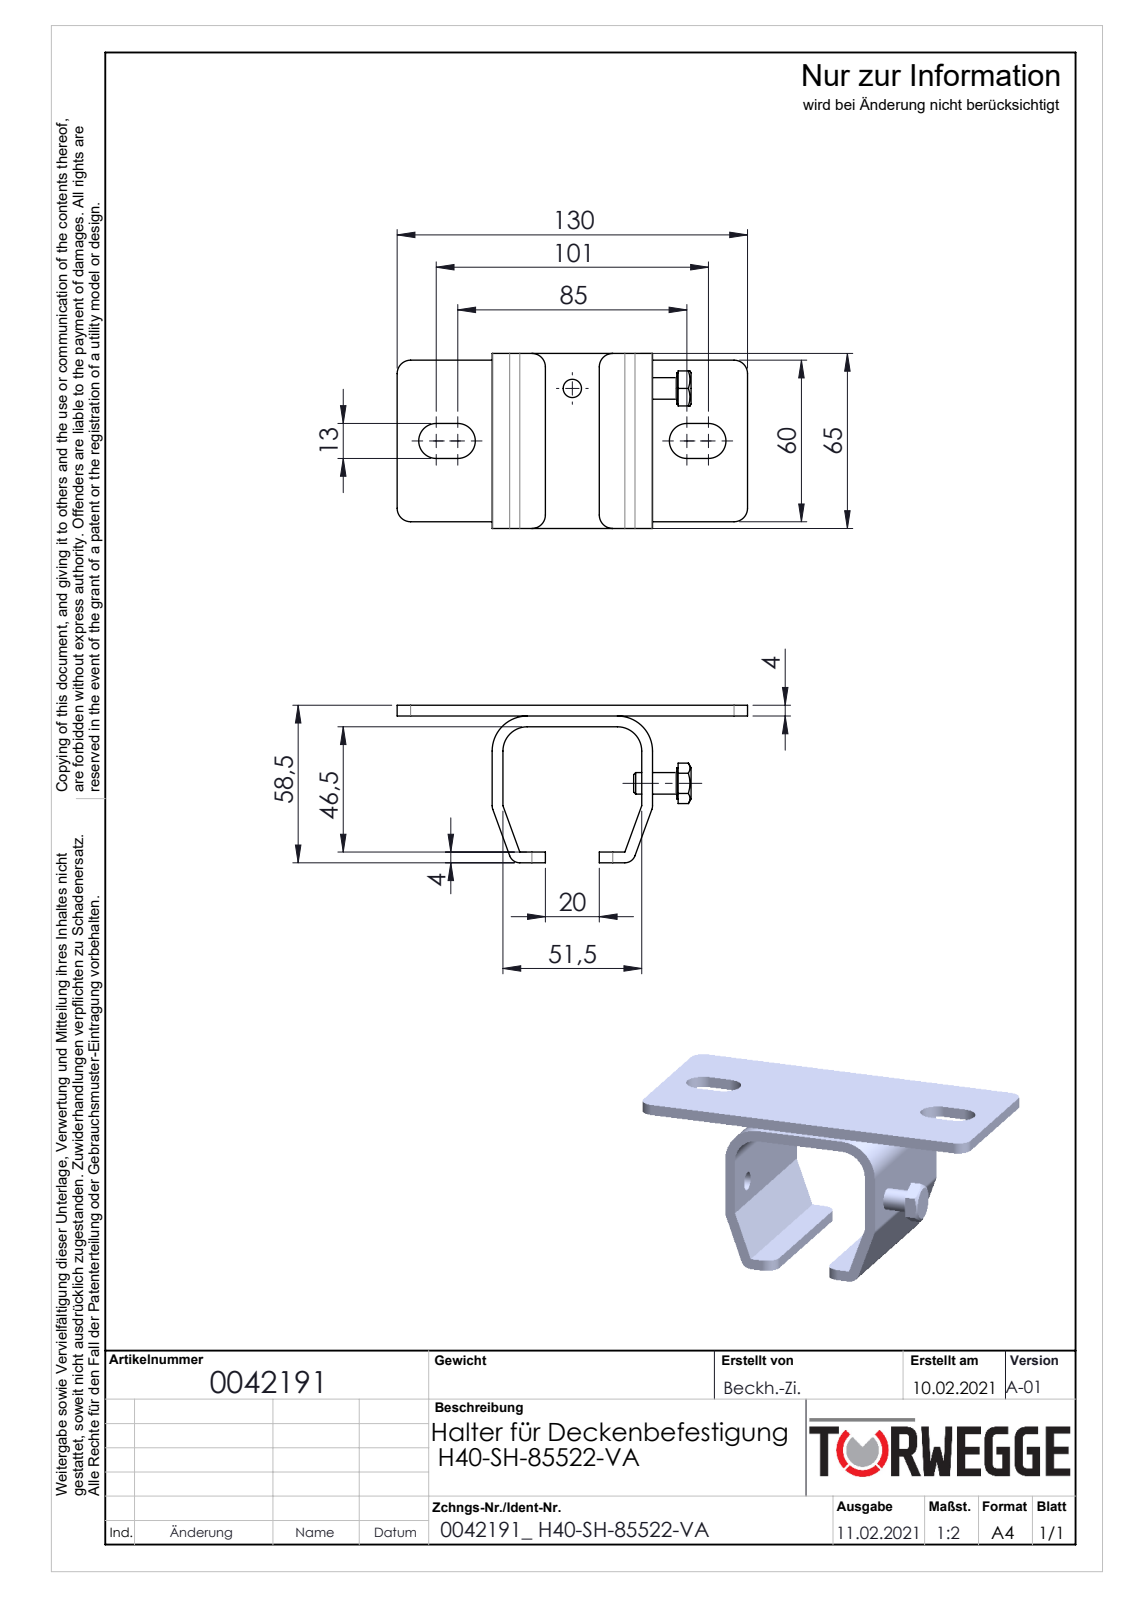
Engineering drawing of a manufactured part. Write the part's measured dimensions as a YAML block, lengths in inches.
part_name: "0042191"
step_written_by: "SolidWorks 2020 (AUTOMOTIVE_DESIGN)"
units: inches
bodies: {solids: 3, faces: 76, planar: 38, cylindrical: 32, other: 6}
overall_size: [5.118, 2.559, 2.303]
volume: 4.551
surface_area: 64.26
round_holes:
  - {diameter: 0.268, count: 2}
round_bosses_or_shafts:
  - {diameter: 0.457, count: 1}
  - {diameter: 0.315, count: 1}
partial_cylinders:
  - {radius: 0.197, count: 8}
  - {radius: 0.157, count: 4}
  - {radius: 0.256, count: 4}
  - {radius: 0.354, count: 2}
  - {radius: 0.512, count: 2}
face_to_face_distances: [0.157, 2.185, 1.988, 2.146, 0.315, 2.343, 2.028, 2.303, 1.831, 0.098]
